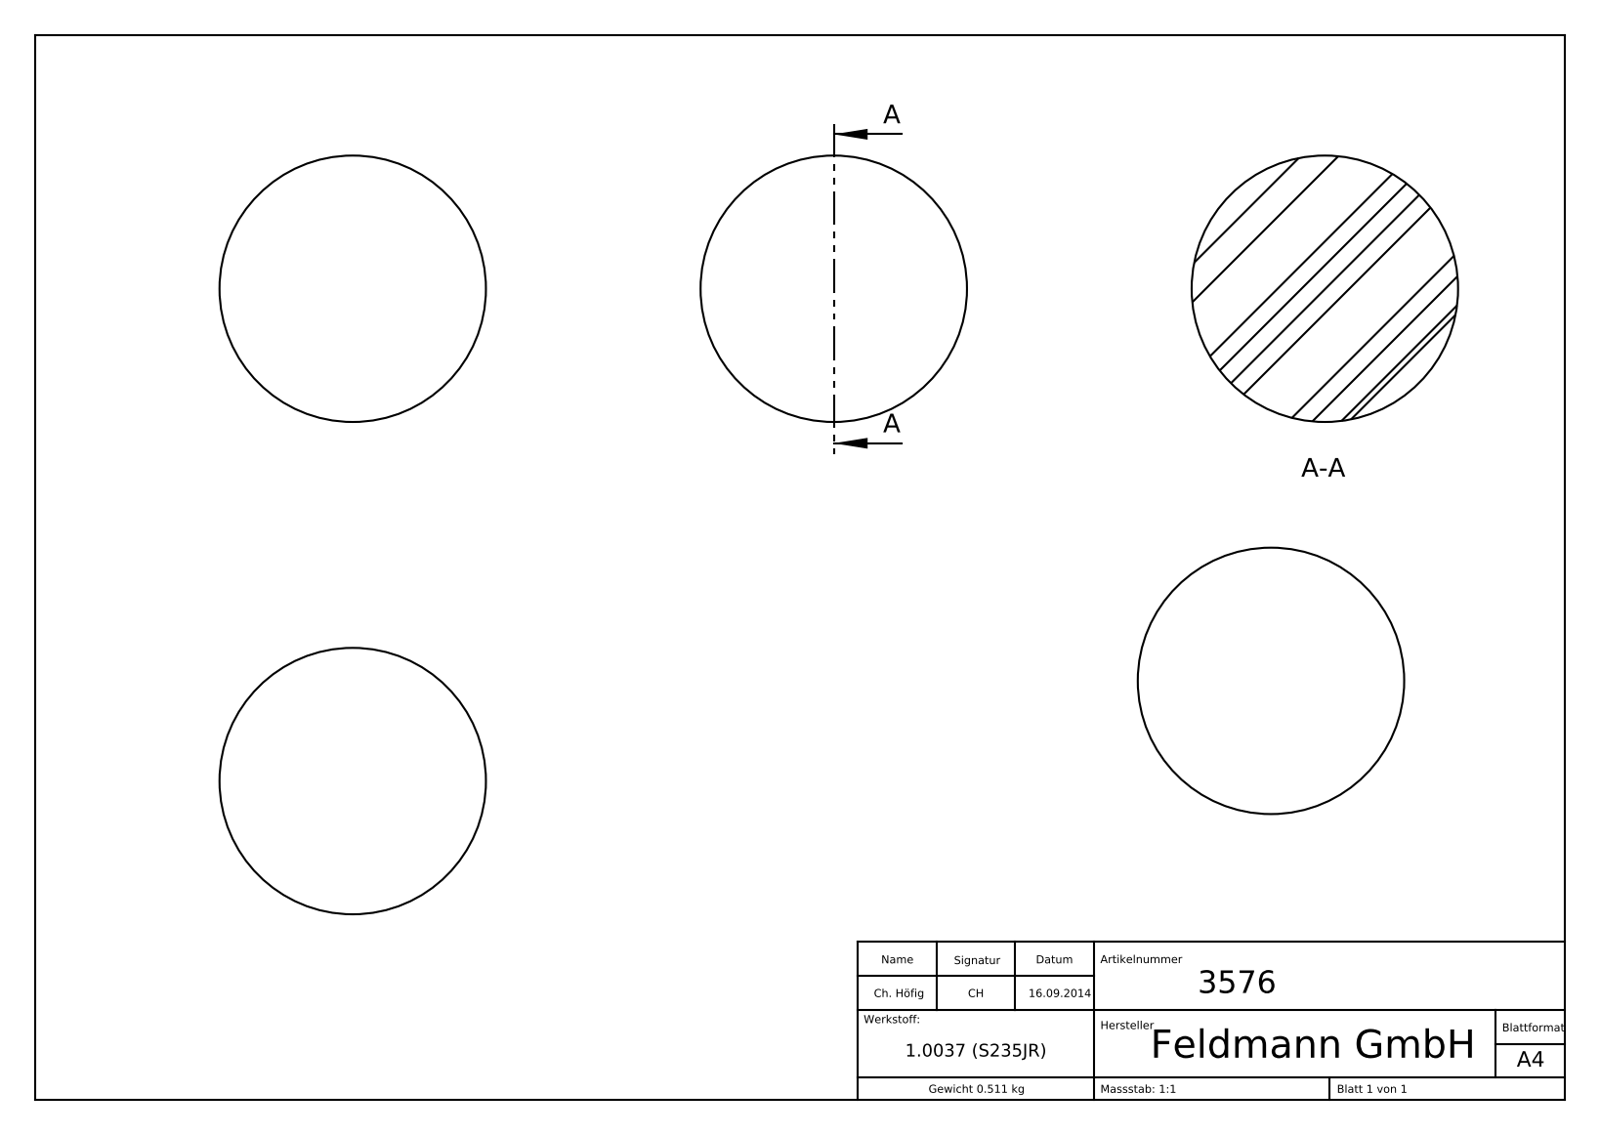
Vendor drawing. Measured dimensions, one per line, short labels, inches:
name: 3576
written by: SolidWorks 2015 (CONFIG_CONTROL_DESIGN)
unit: in
bodies: 1 solid, 2 faces (0 planar, 0 cylindrical, 2 other)
size: 1.969 × 1.969 × 1.969
volume: 3.994 in³; area: 12.17 in²
